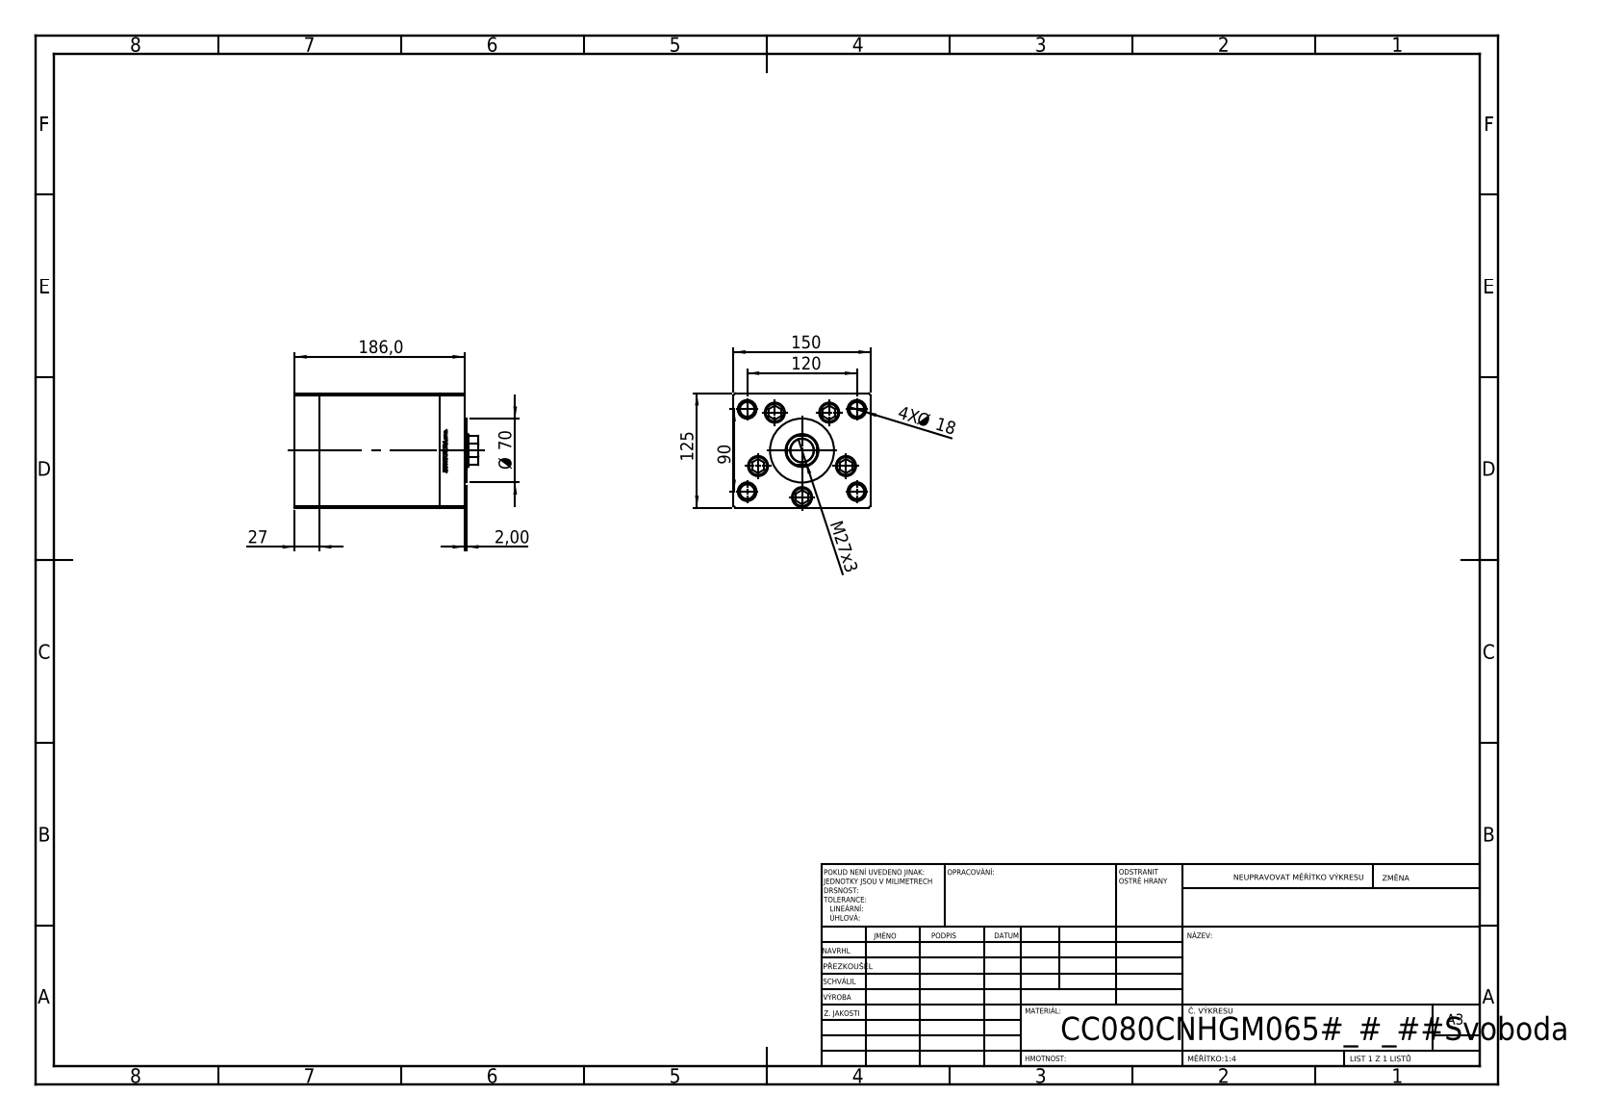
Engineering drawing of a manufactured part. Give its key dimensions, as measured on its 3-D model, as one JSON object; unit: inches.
{"part_name": "V220C FRONT; V220C BACK_C; V220C_C MIDDLE; V220C_VC_C (+1 more)", "step_written_by": "SolidWorks 2019 (CONFIG_CONTROL_DESIGN)", "units": "inches", "bodies": {"solids": 13, "faces": 1186, "planar": 545, "cylindrical": 179, "other": 462}, "overall_size": [7.913, 5.906, 4.921], "volume_in3": 177.9, "surface_area_in2": 562.6, "round_holes": [[0.689, 9], [0.866, 5], [0.079, 4], [0.518, 4], [0.63, 4], [0.807, 4], [0.827, 1], [1.004, 1], [1.417, 1]], "round_bosses_or_shafts": [[0.315, 5], [0.827, 4], [3.15, 1], [2.756, 1]], "partial_cylinders_radius": [[0.037, 2], [0.689, 1]], "face_to_face_distances": [1.063, 6.26, 5.197, 5.906, 4.921, 1.319, 7.323, 0.256, 6.004, 4.941], "hole_center_spacings": [2.008, 2.953, 1.198, 1.2, 2.319, 2.374, 2.411, 2.486]}
